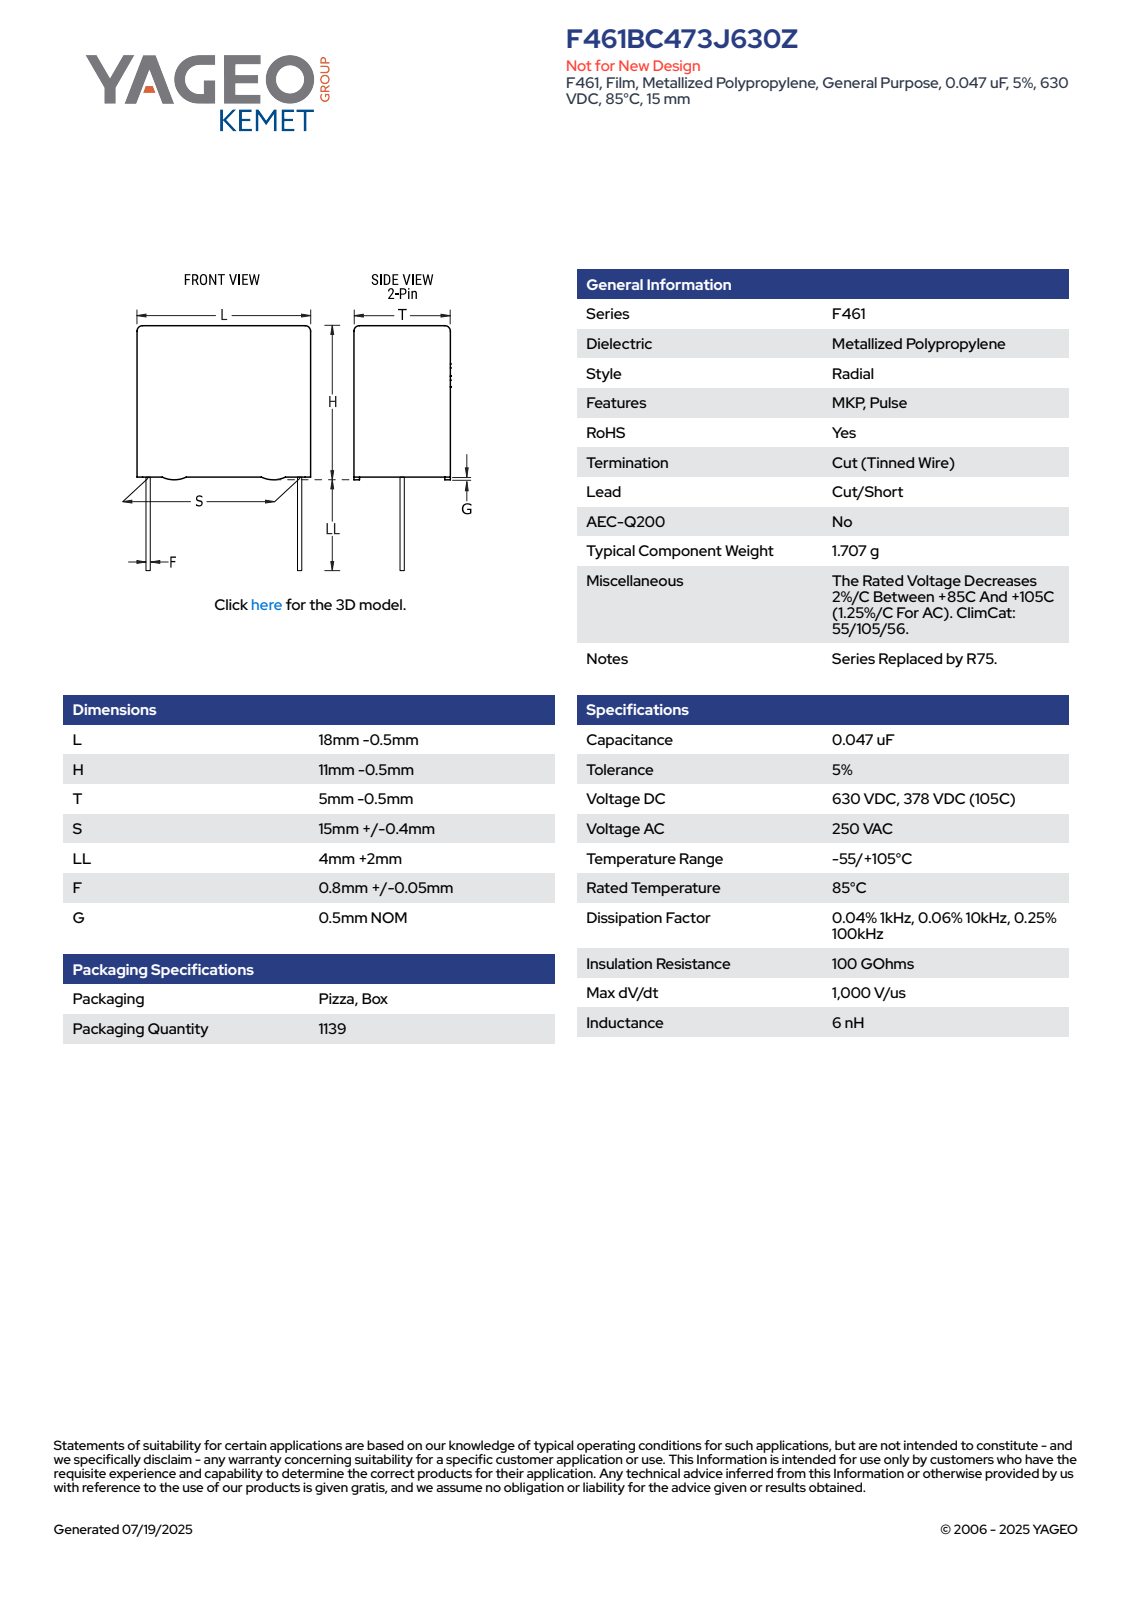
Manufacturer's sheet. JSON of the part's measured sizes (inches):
{"part_name": "CFR_RBG_18X11X5_L17.5H10.5T4.5S15LL6F0.85G0.5", "step_written_by": "SolidWorks 2014 (AUTOMOTIVE_DESIGN)", "units": "inches", "bodies": {"solids": 4, "faces": 89, "planar": 81, "cylindrical": 8, "other": 0}, "overall_size": [0.689, 0.65, 0.177], "volume_in3": 0.048, "surface_area_in2": 1.04, "round_bosses_or_shafts": [[0.033, 2]], "partial_cylinders_radius": [[0.02, 4]], "face_to_face_distances": [0.177, 0.394, 0.689, 0.167, 0.157, 0.02, 0.413, 0.236, 0.256, 0.65]}
